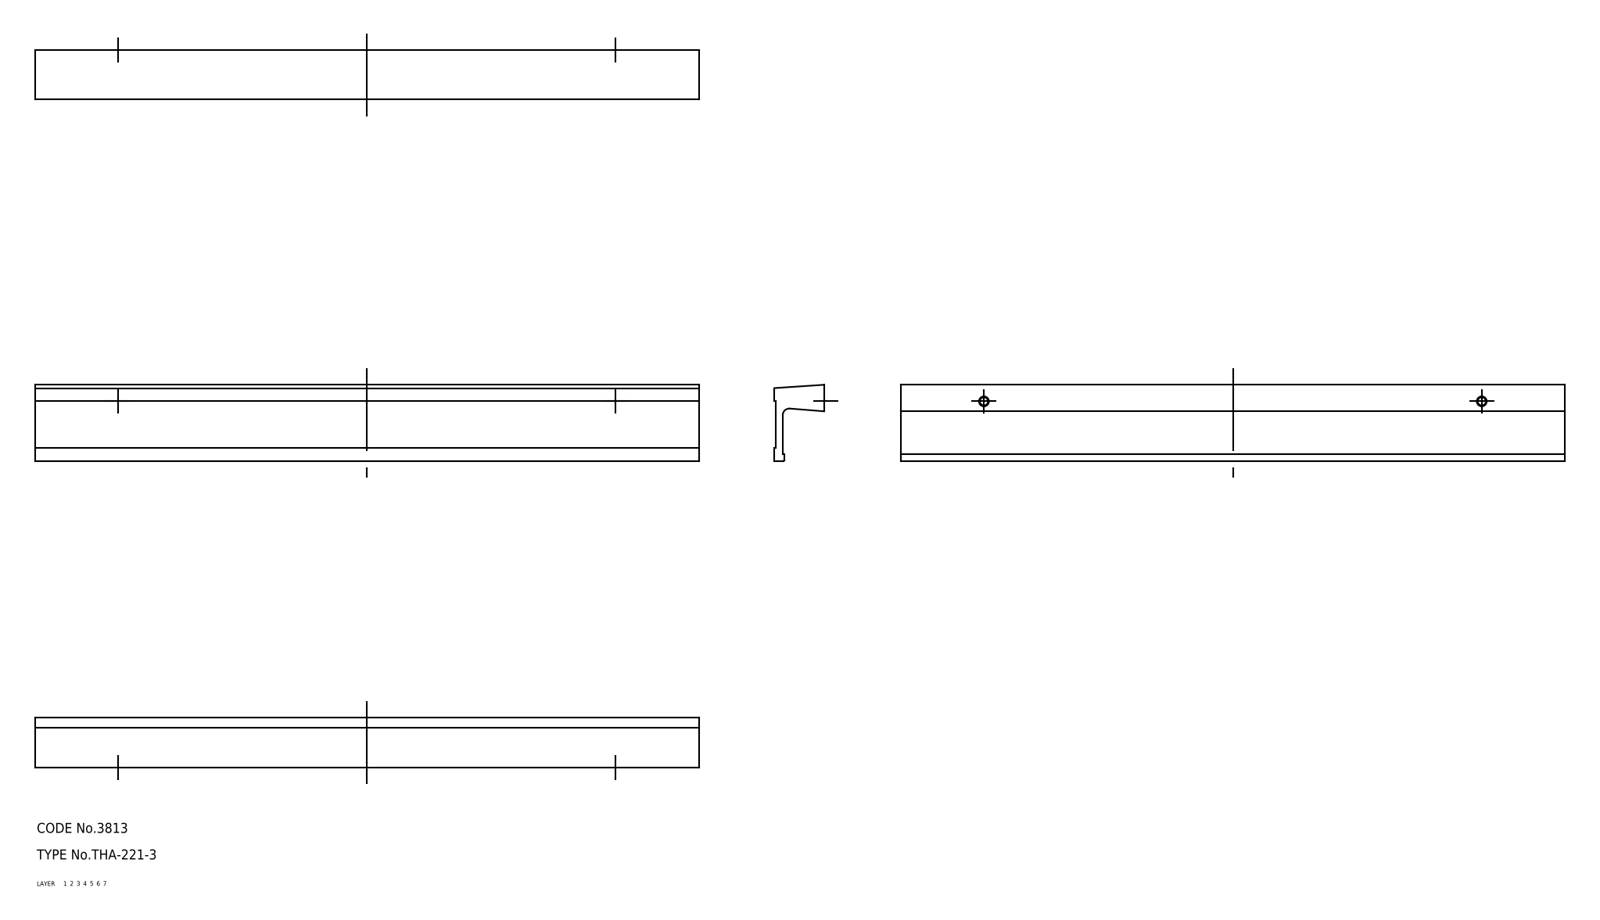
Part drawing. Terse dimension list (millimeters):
name: pull
written by: CADfix (AUTOMOTIVE_DESIGN)
unit: mm
bodies: 1 solid, 22 faces (0 planar, 0 cylindrical, 22 other)
size: 200 × 23 × 15
volume: 27 606 mm³; area: 15 839 mm²
